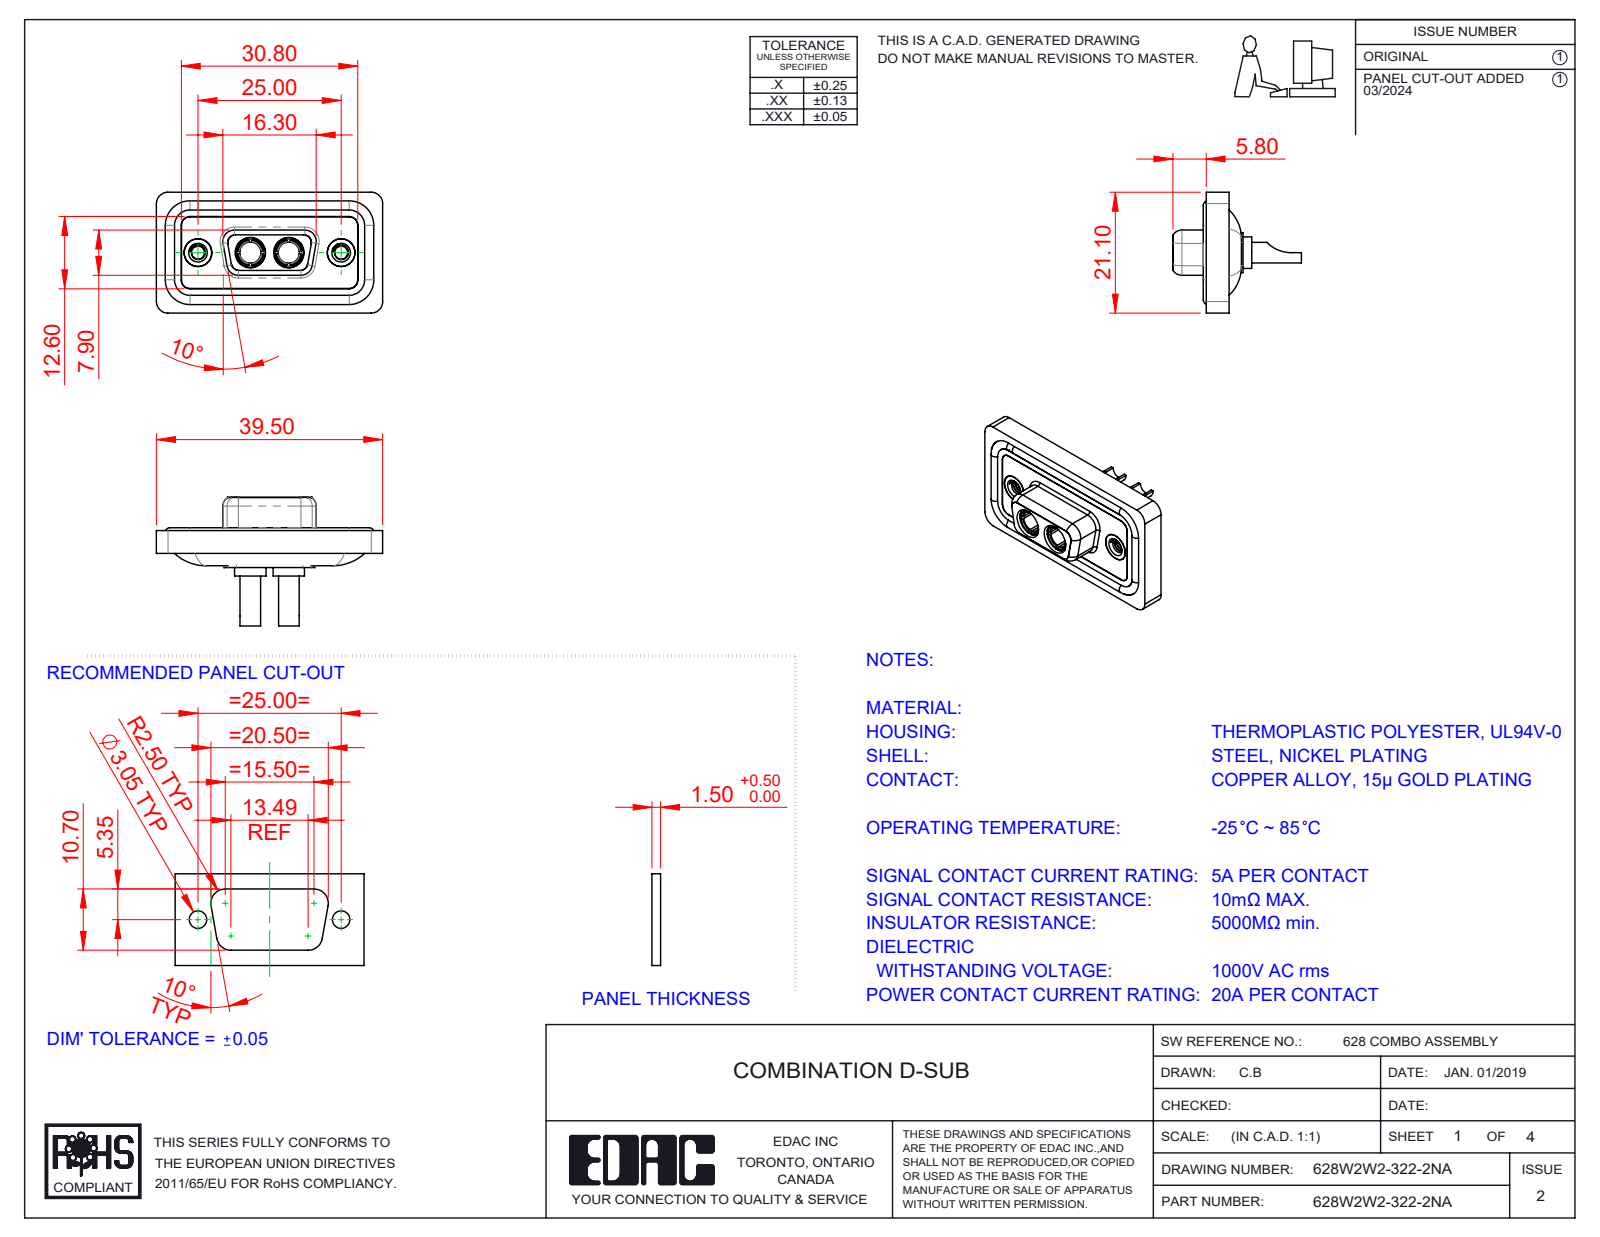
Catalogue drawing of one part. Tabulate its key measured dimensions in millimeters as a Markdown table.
| quantity | value |
| --- | --- |
| part name | 628W2W2-322-2NA; 628Combo Threaded Rivet_A; 628Combo Shell Front_09 Contacts; 628Combo Waterproof Housing_09 Contacts (+3 more) |
| STEP written by | SolidWorks 2023 (CONFIG_CONTROL_DESIGN) |
| units | millimeters |
| bodies | 11 solids, 544 faces (169 planar, 242 cylindrical, 133 other) |
| overall size | 39.5 × 22.45 × 21.1 |
| volume | 4 740 mm³ |
| surface area | 7 798 mm² |
| round holes (diameter × count) | 4.85 × 4, 2.26 × 2, 2.7 × 2, 3.7 × 2, 4 × 2, 4.05 × 2, 5 × 2, 5.3 × 2 |
| round bosses / shafts (diameter × count) | 1.6 × 4, 5.5 × 2, 5.2 × 2, 4.96 × 2, 4.95 × 2, 4.8 × 2, 4.75 × 2, 3.75 × 2 |
| partial cylindrical surfaces (radius × count) | 1.5 × 22, 2 × 18, 1.35 × 8, 1.6 × 8, 0.25 × 4, 0.5 × 4, 0.6 × 4, 0.65 × 4 |
| main face-to-face distances | 0.4, 1.8, 1.1, 2.9, 0.5, 1.6, 5.65, 7.45, 5.35, 1.5 |
| hole center spacings | 9.14, 15.86, 6.72, 25 |
